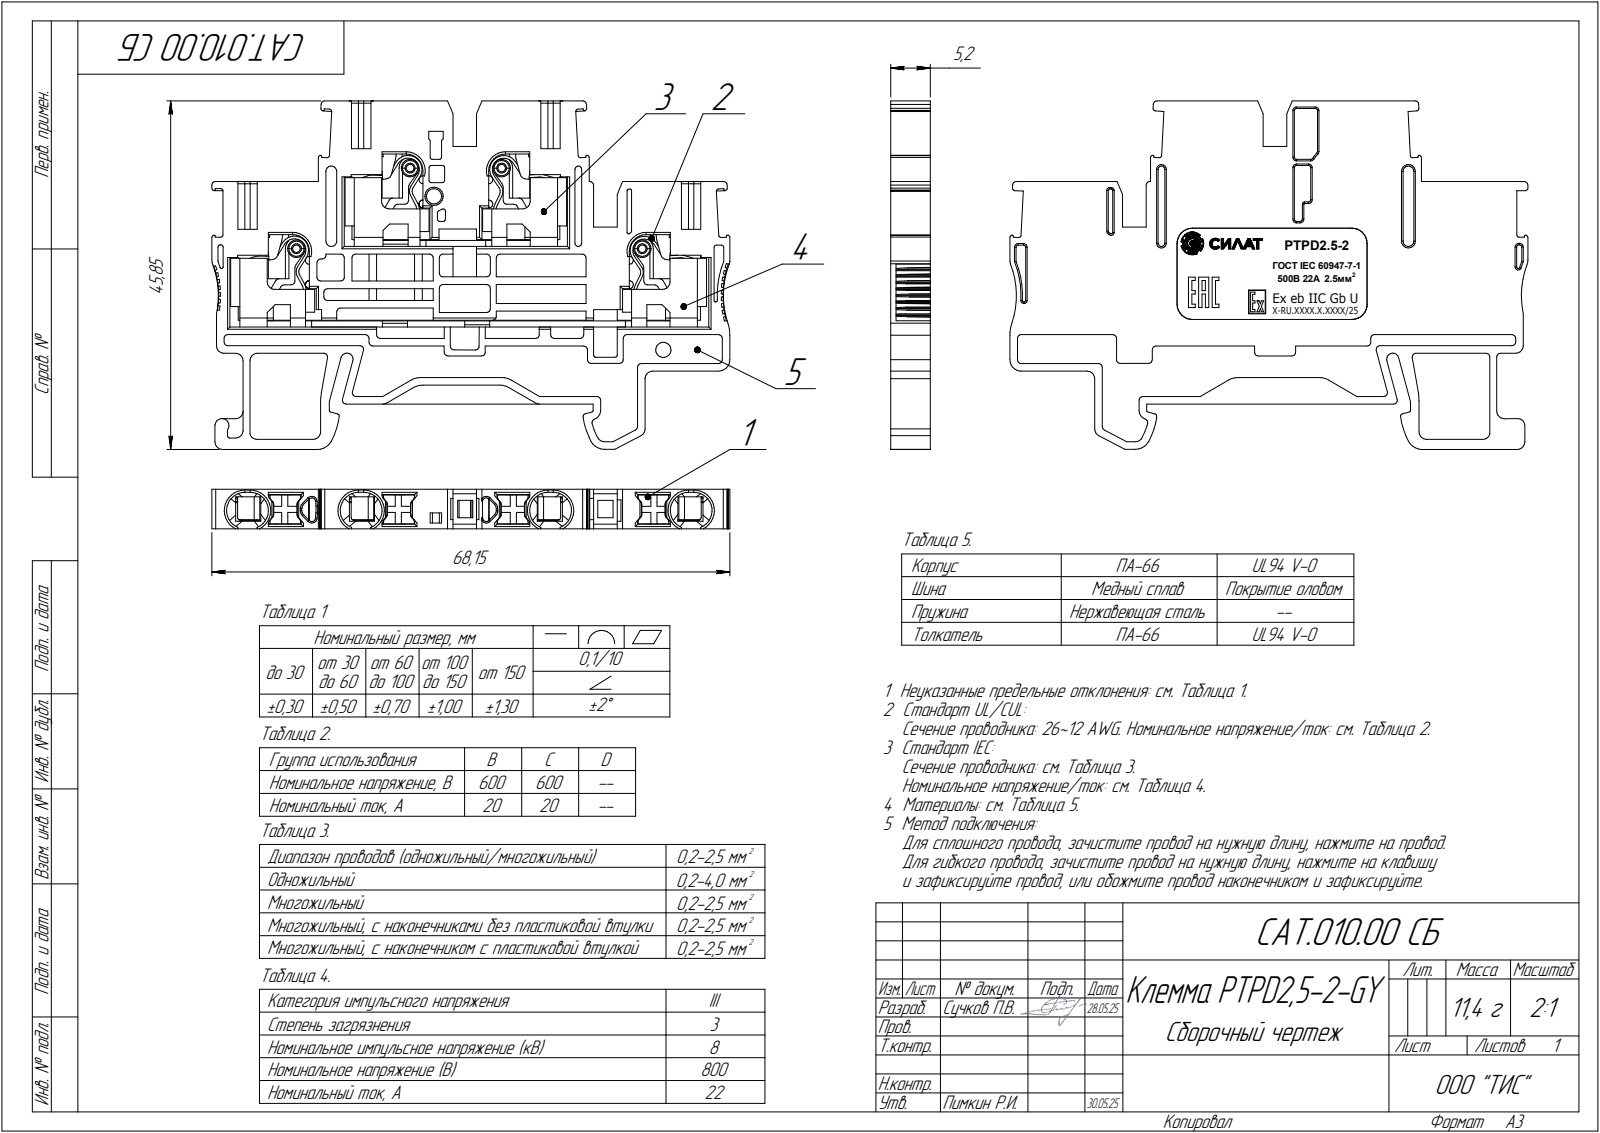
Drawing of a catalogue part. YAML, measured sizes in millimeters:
part_name: "Клемма PTPD2,5-2-GY"
step_written_by: "SolidWorks 2024 (AUTOMOTIVE_DESIGN)"
units: millimeters
bodies: {solids: 1, faces: 536, planar: 370, cylindrical: 158, other: 8}
overall_size: [68.15, 45.85, 5.2]
volume: 10869
surface_area: 6525
partial_cylinders:
  - {radius: 0.3, count: 51}
  - {radius: 0.5, count: 45}
  - {radius: 1, count: 9}
  - {radius: 0.15, count: 8}
  - {radius: 2.4, count: 8}
  - {radius: 0.2, count: 4}
  - {radius: 0.75, count: 4}
  - {radius: 5, count: 3}
face_to_face_distances: [5.2, 10.6, 4.64, 39.88, 29.28, 5.97, 35.25, 45.85, 12.65, 6.68]
